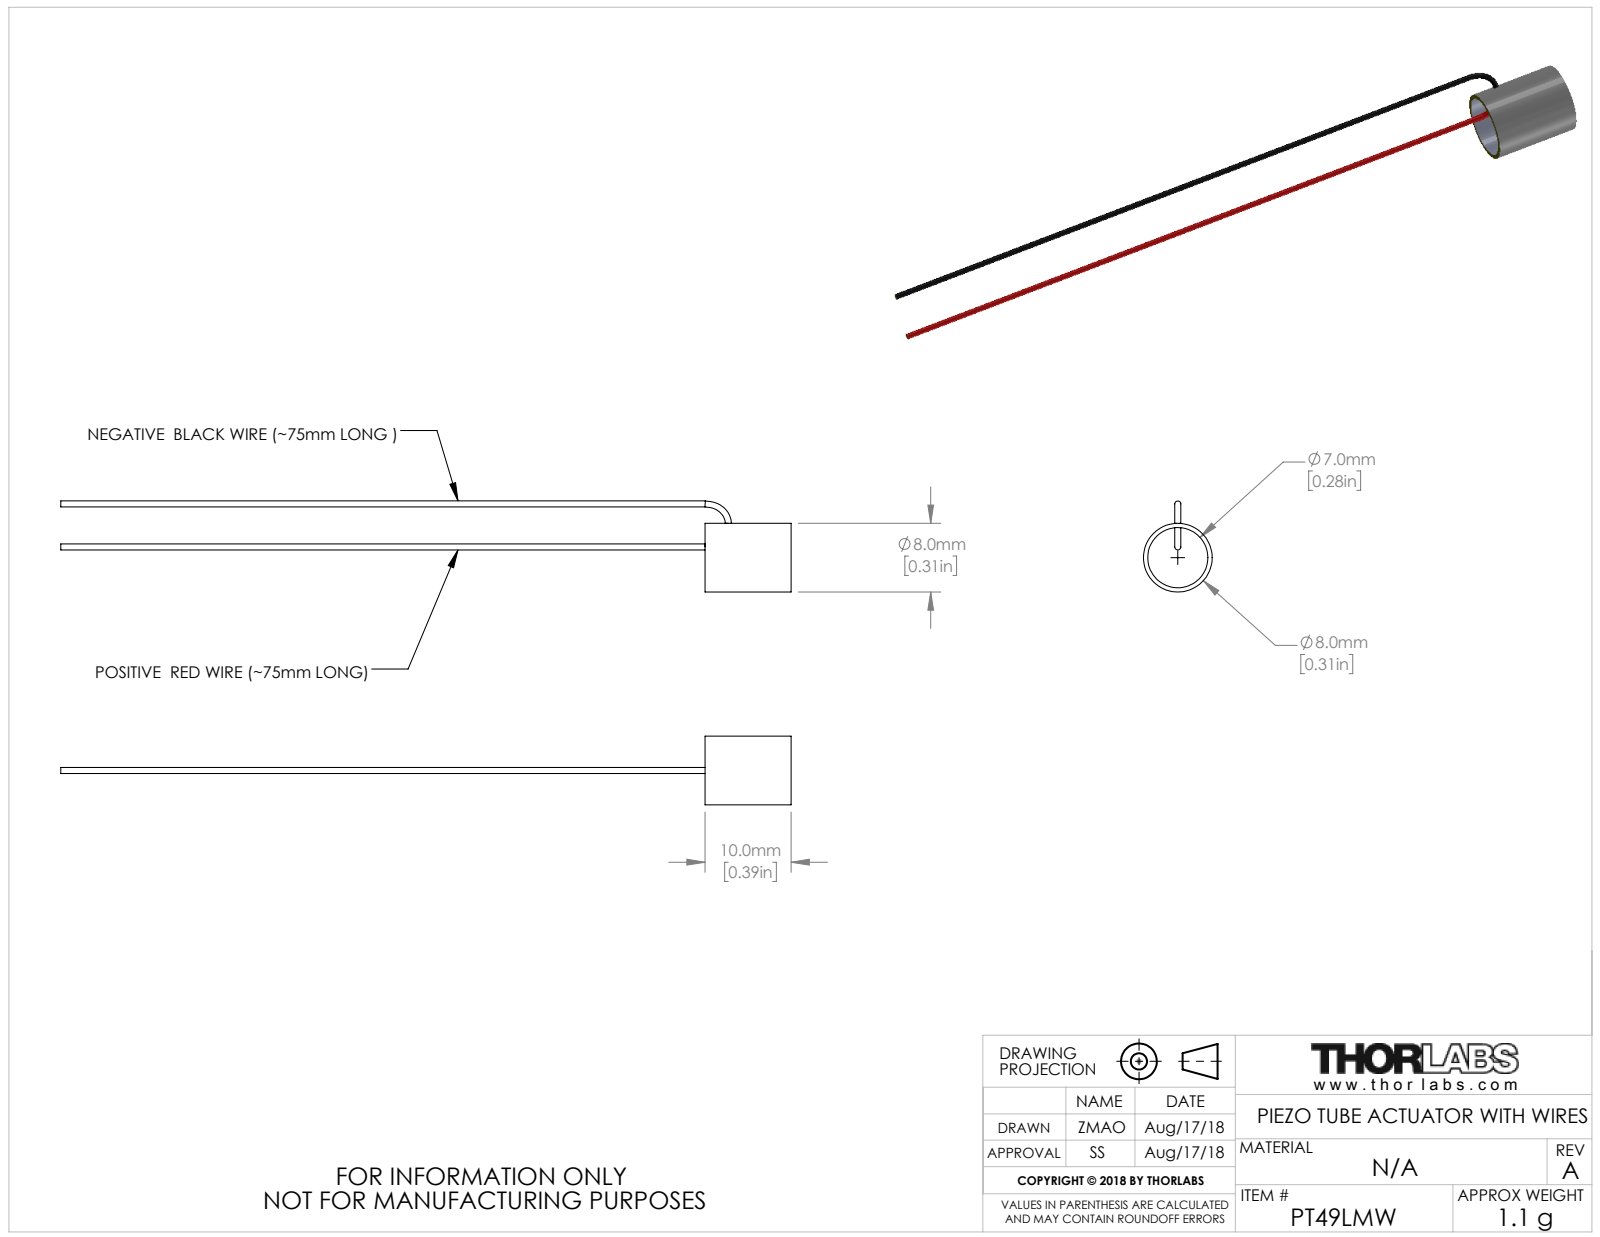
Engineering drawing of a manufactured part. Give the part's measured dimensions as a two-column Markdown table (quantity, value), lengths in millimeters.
| quantity | value |
| --- | --- |
| part name | CTN011969 |
| STEP written by | SolidWorks 2018 (AUTOMOTIVE_DESIGN) |
| units | millimeters |
| bodies | 1 solid, 18 faces (6 planar, 8 cylindrical, 4 other) |
| overall size | 85 × 10.6 × 8 |
| volume | 179 mm³ |
| surface area | 843 mm² |
| round holes (diameter × count) | 7 × 1 |
| round bosses / shafts (diameter × count) | 0.7 × 2, 8 × 1 |
| main face-to-face distances | 10, 75, 85 |
